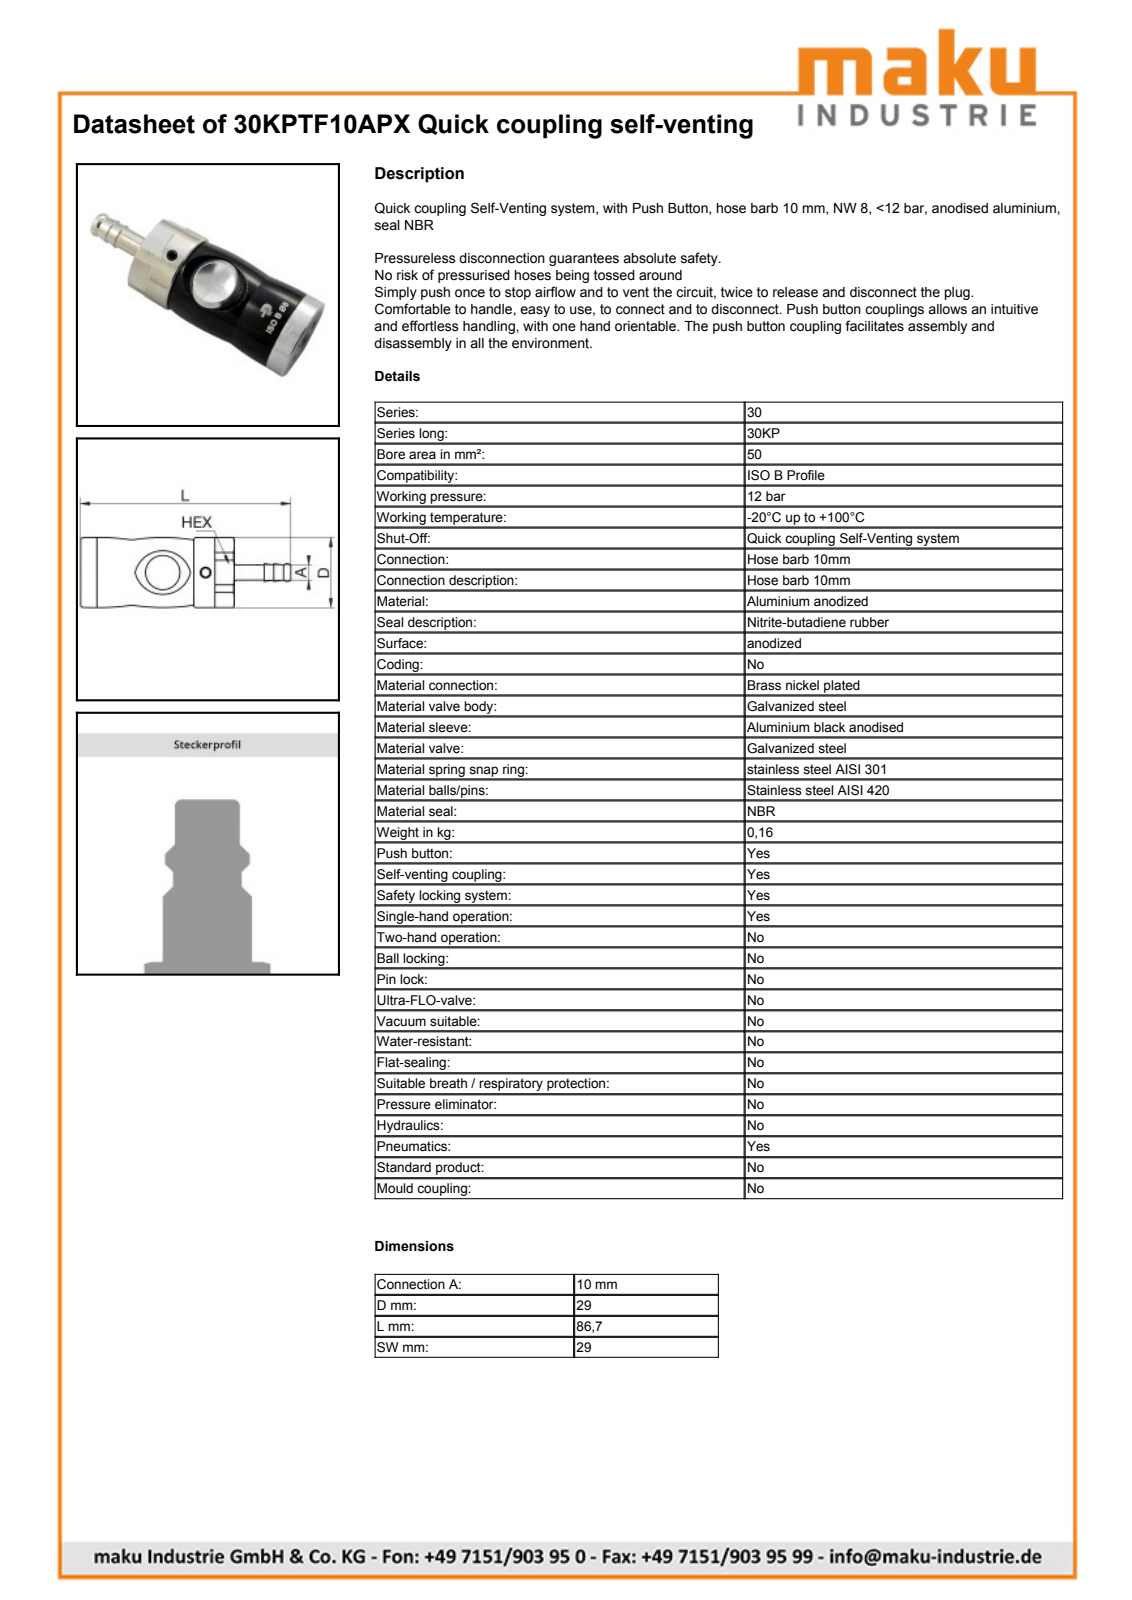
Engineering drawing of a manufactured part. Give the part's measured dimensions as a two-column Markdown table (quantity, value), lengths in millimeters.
| quantity | value |
| --- | --- |
| STEP written by | Autodesk Inventor 2019 (CONFIG_CONTROL_DESIGN) |
| units | millimeters |
| bodies | 42 solids, 243 faces (74 planar, 74 cylindrical, 95 other) |
| overall size | 86.7 × 29.04 × 29.04 |
| volume | 47 468 mm³ |
| surface area | 28 194 mm² |
| round holes (diameter × count) | 3.5 × 1, 8 × 1, 8.5 × 1, 11.2 × 1, 12.2 × 1, 14 × 1, 15.3 × 1, 16 × 1, 17.5 × 1, 18.1 × 1, 20.6 × 1, 20.7 × 1 |
| round bosses / shafts (diameter × count) | 29 × 1, 26 × 1, 24.95 × 1, 24.5 × 1, 24 × 1, 20.5 × 1, 18.2 × 1, 18 × 1 |
| partial cylindrical surfaces (radius × count) | 2.5 × 4, 7.1 × 2 |
| main face-to-face distances | 63.4, 40, 16.7, 46.7, 6.7, 56.7, 27, 62.8, 46.1, 6.1 |
| hole center spacings | 17.65 |
